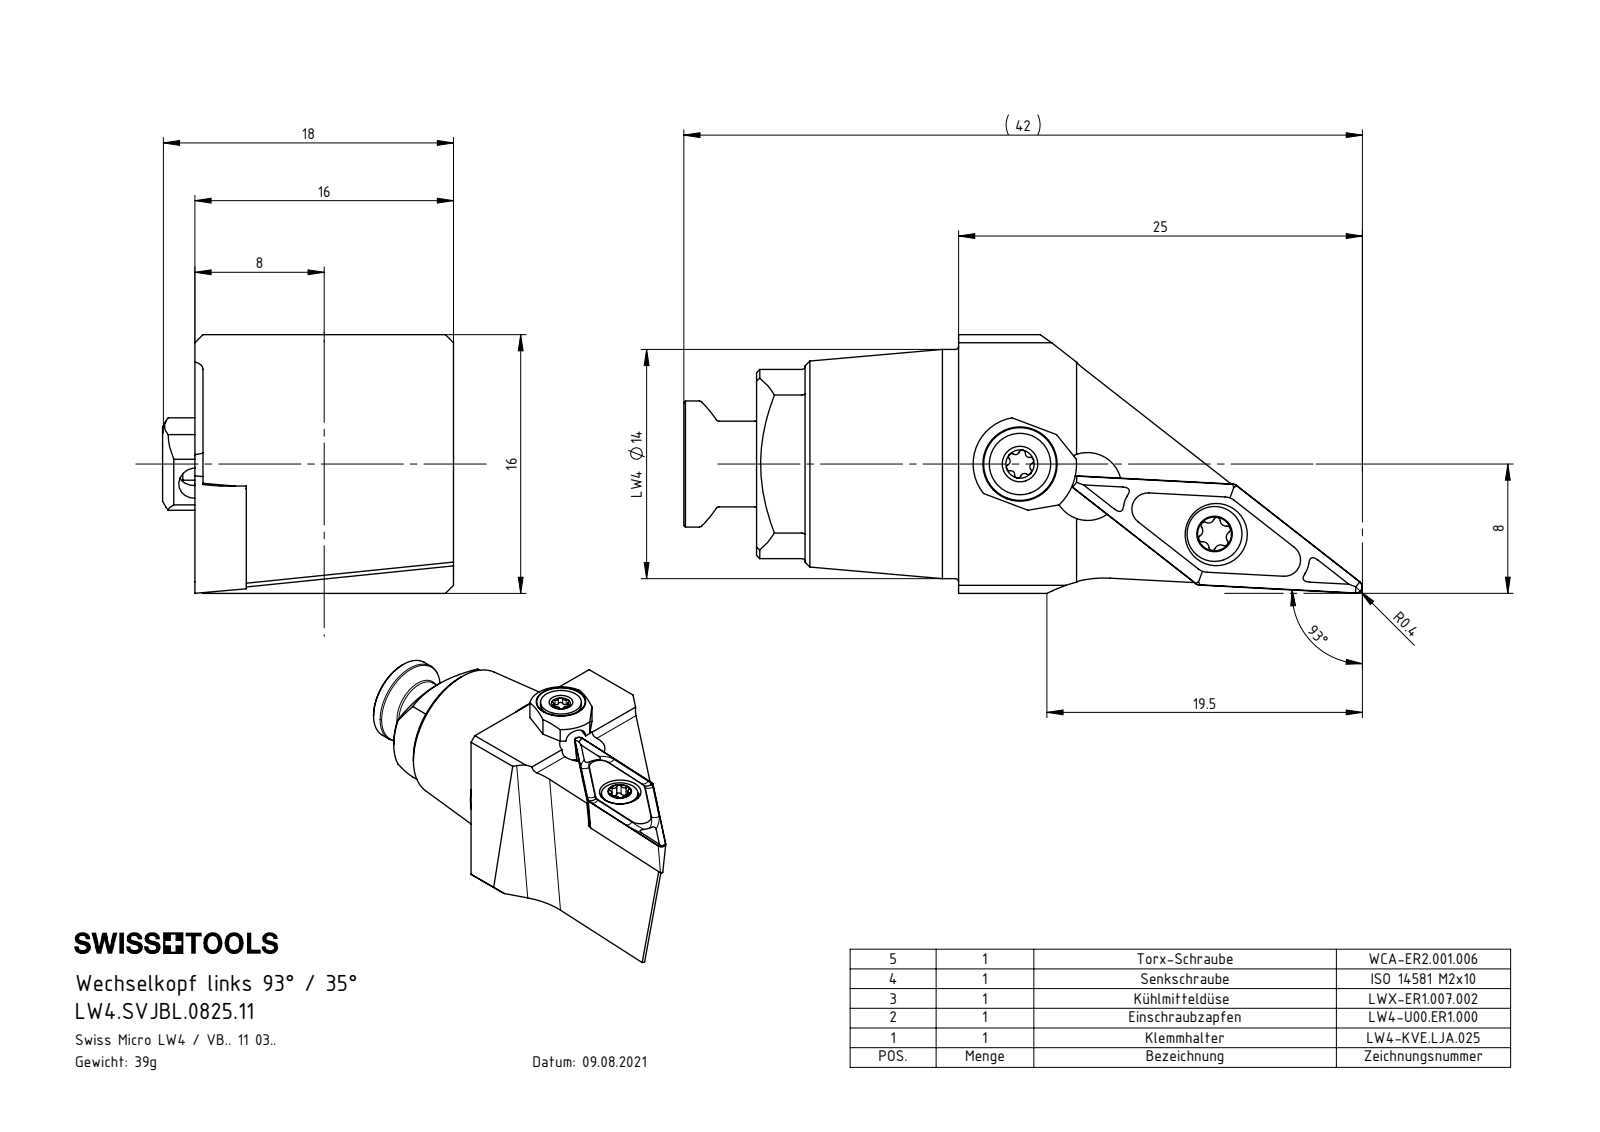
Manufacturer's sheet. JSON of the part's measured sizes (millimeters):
{"part_name": "VBMT110304; WCA-ER2.001.006_A; LW4-KVE.LJA.025_A; ISO 14581 - M2x10 (+1 more)", "step_written_by": "SolidWorks 2022 (CONFIG_CONTROL_DESIGN)", "units": "millimeters", "bodies": {"solids": 4, "faces": 204, "planar": 56, "cylindrical": 67, "other": 81}, "overall_size": [37.48, 17.95, 16], "volume_mm3": 4502, "surface_area_mm2": 2722, "round_holes": [[2, 2], [1.6, 1], [2.05, 1], [2.8, 1], [3, 1], [3.85, 1], [4.2, 1], [5.5, 1]], "round_bosses_or_shafts": [[14.17, 1], [3.8, 1], [3.4, 1], [2.5, 1], [2, 1]], "partial_cylinders_radius": [[0.2, 8], [0.21, 6], [0.24, 6], [0.36, 4], [0.36, 2], [0.5, 1], [5.85, 1], [7, 1]], "face_to_face_distances": [16, 12.82, 3.18, 15.5, 2.68, 0.5, 12.5, 4, 12, 3], "hole_center_spacings": [4.41, 8.38, 8.49, 12.79, 12.9]}
